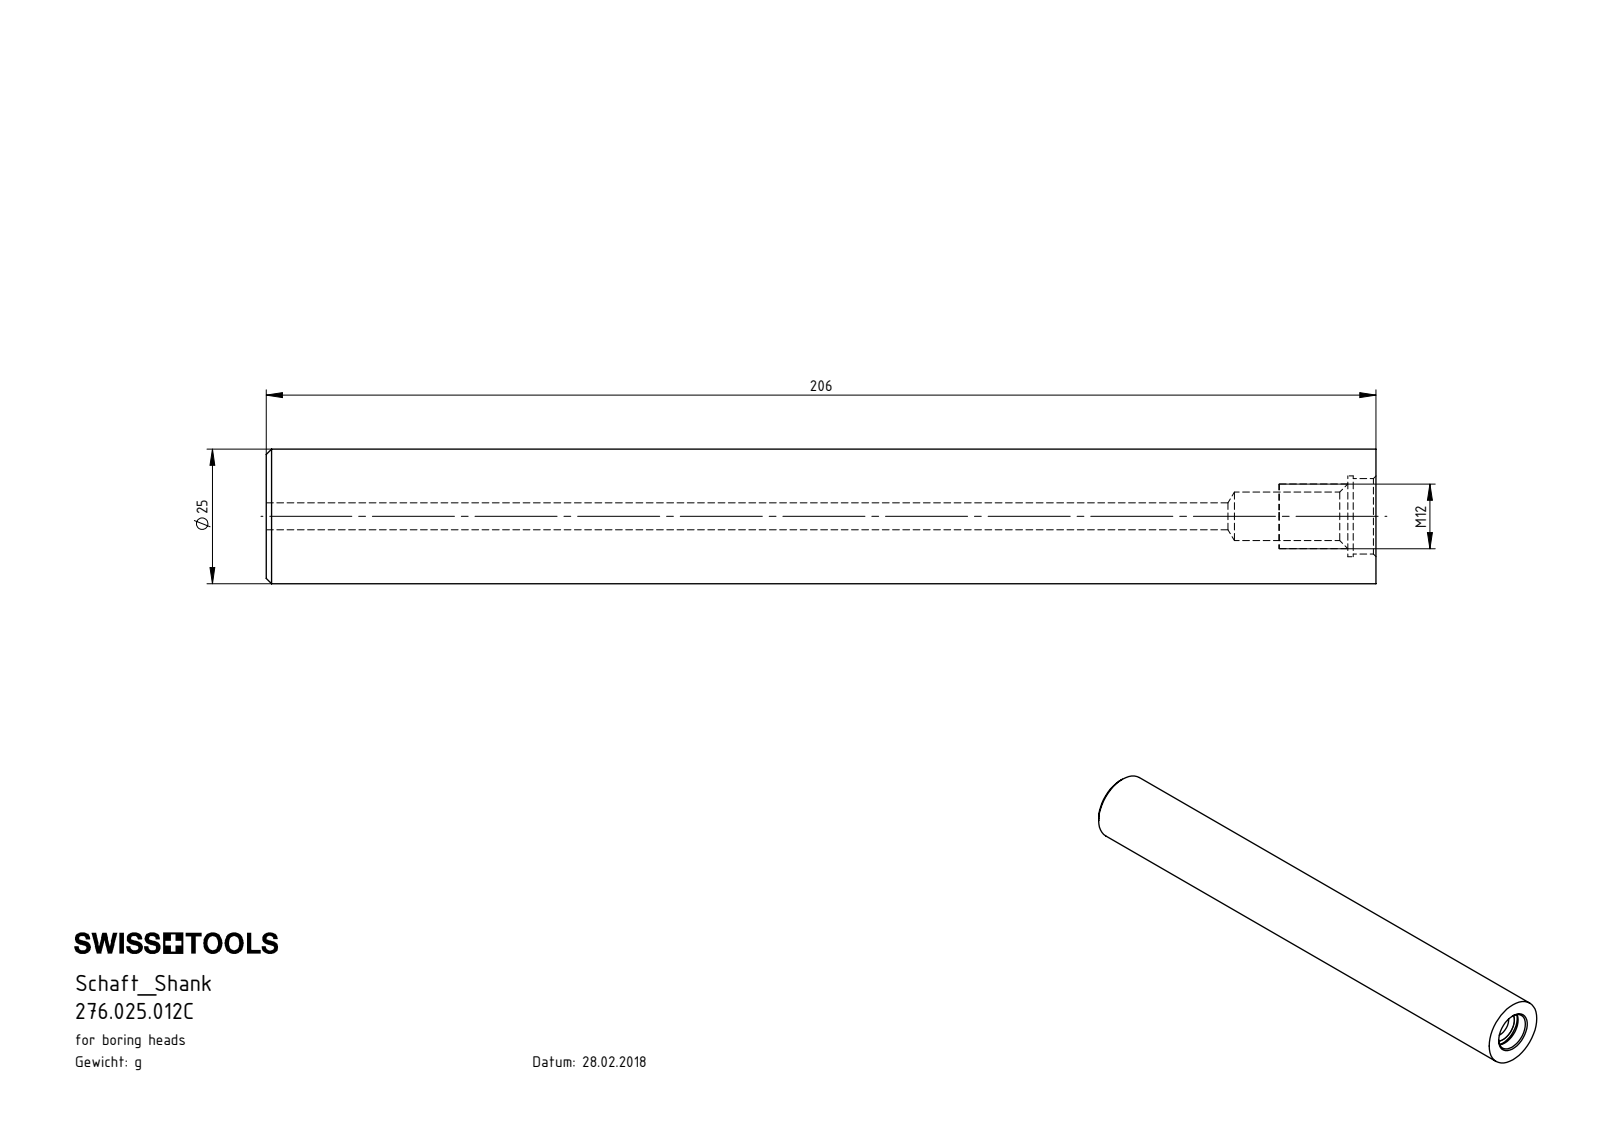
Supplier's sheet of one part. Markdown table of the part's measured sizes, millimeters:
| quantity | value |
| --- | --- |
| part name | 276.025.012C |
| STEP written by | SolidWorks 2017 (CONFIG_CONTROL_DESIGN) |
| units | millimeters |
| bodies | 1 solid, 22 faces (4 planar, 10 cylindrical, 8 other) |
| overall size | 206 × 25 × 25 |
| volume | 95 318 mm³ |
| surface area | 20 726 mm² |
| round holes (diameter × count) | 5 × 1, 9 × 1, 14 × 1, 15 × 1 |
| round bosses / shafts (diameter × count) | 25 × 1 |
| main face-to-face distances | 206, 200.75, 5.25, 201.75, 1, 4.25 |
